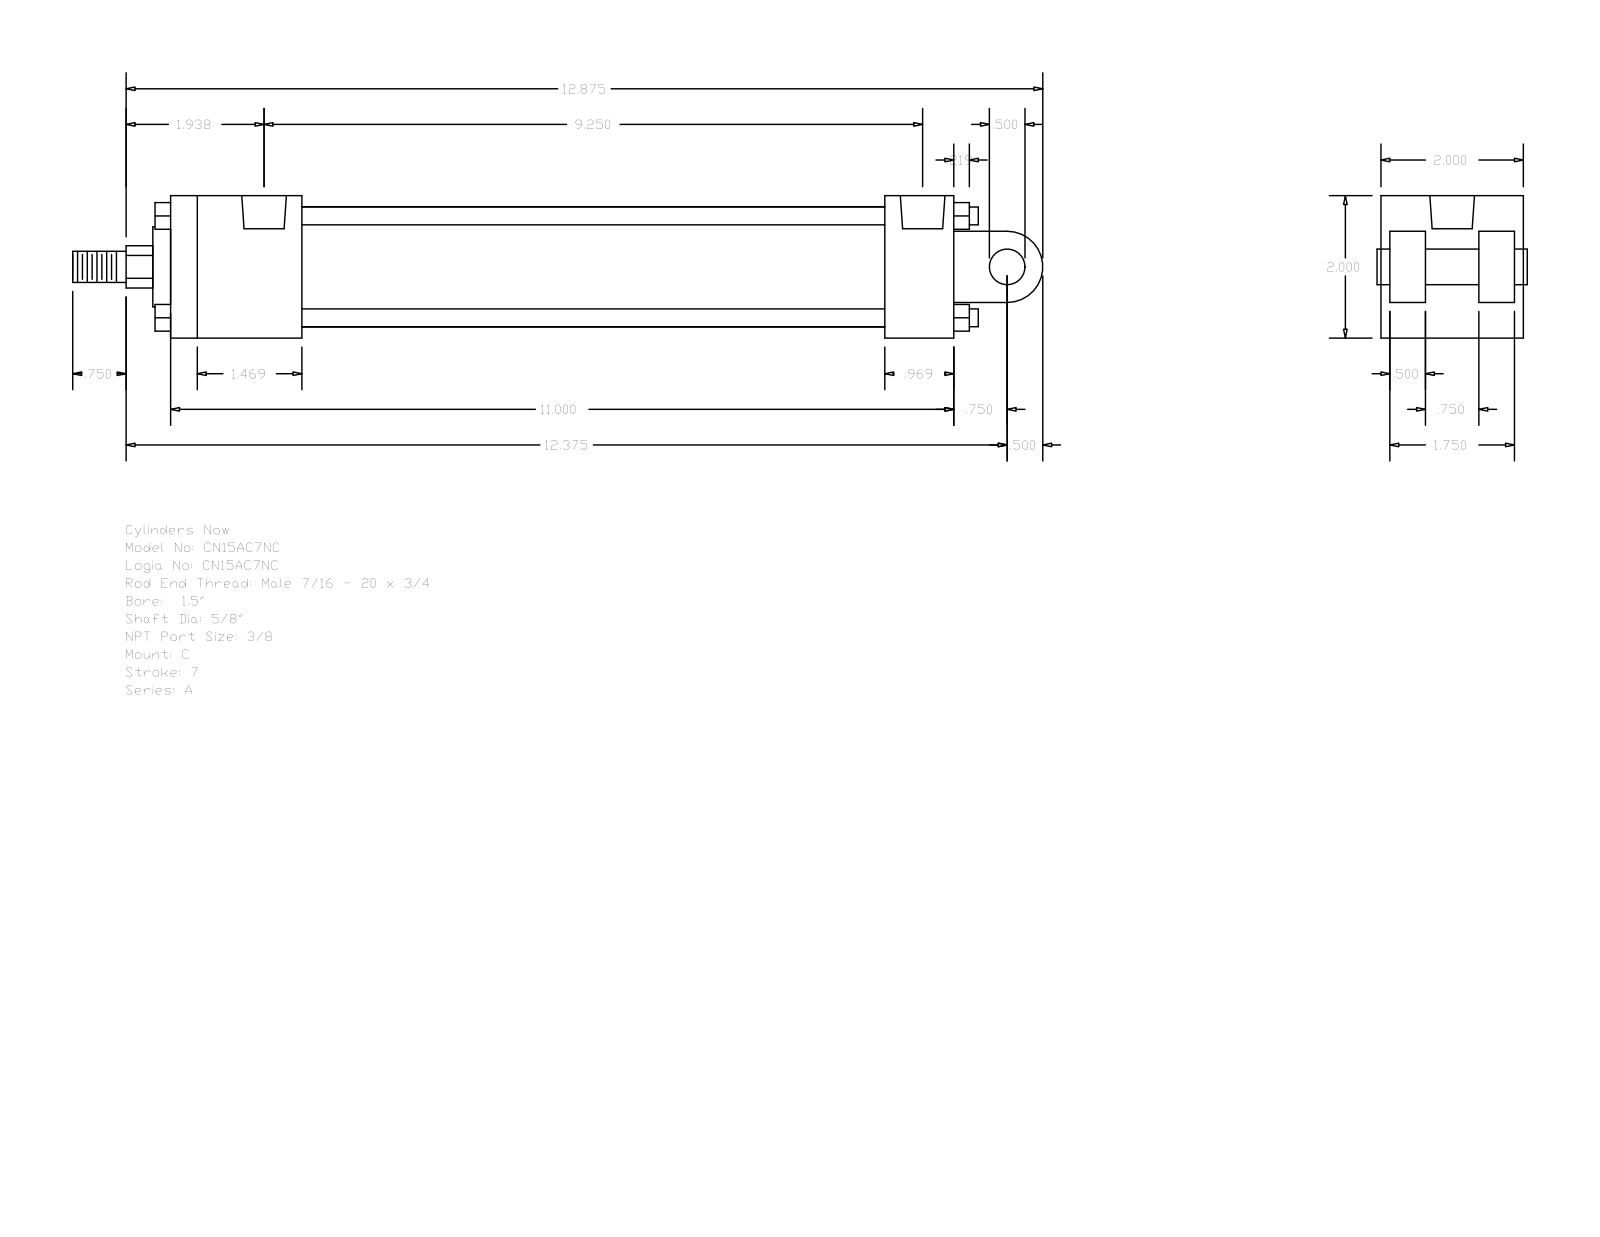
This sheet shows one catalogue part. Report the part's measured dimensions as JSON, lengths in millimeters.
{"part_name": "A_C__0150_0.625", "step_written_by": "GSSL Pune (CONFIG_CONTROL_DESIGN)", "units": "millimeters", "bodies": {"solids": 0, "faces": 135, "planar": 102, "cylindrical": 33, "other": 0}, "overall_size": [346.07, 50.8, 50.8], "round_holes": [[5.56, 4], [15.93, 2]], "round_bosses_or_shafts": [[6.35, 4], [42.93, 1], [28.57, 1], [15.88, 1], [12.7, 1], [11.11, 1]], "partial_cylinders_radius": [[7.54, 1], [12.7, 1]], "face_to_face_distances": [50.8, 12.7, 279.39, 34.93, 3.17, 15.87, 47.63, 31.76, 254.79, 24.6], "hole_center_spacings": [3.97, 227.01, 230.98, 234.95]}
